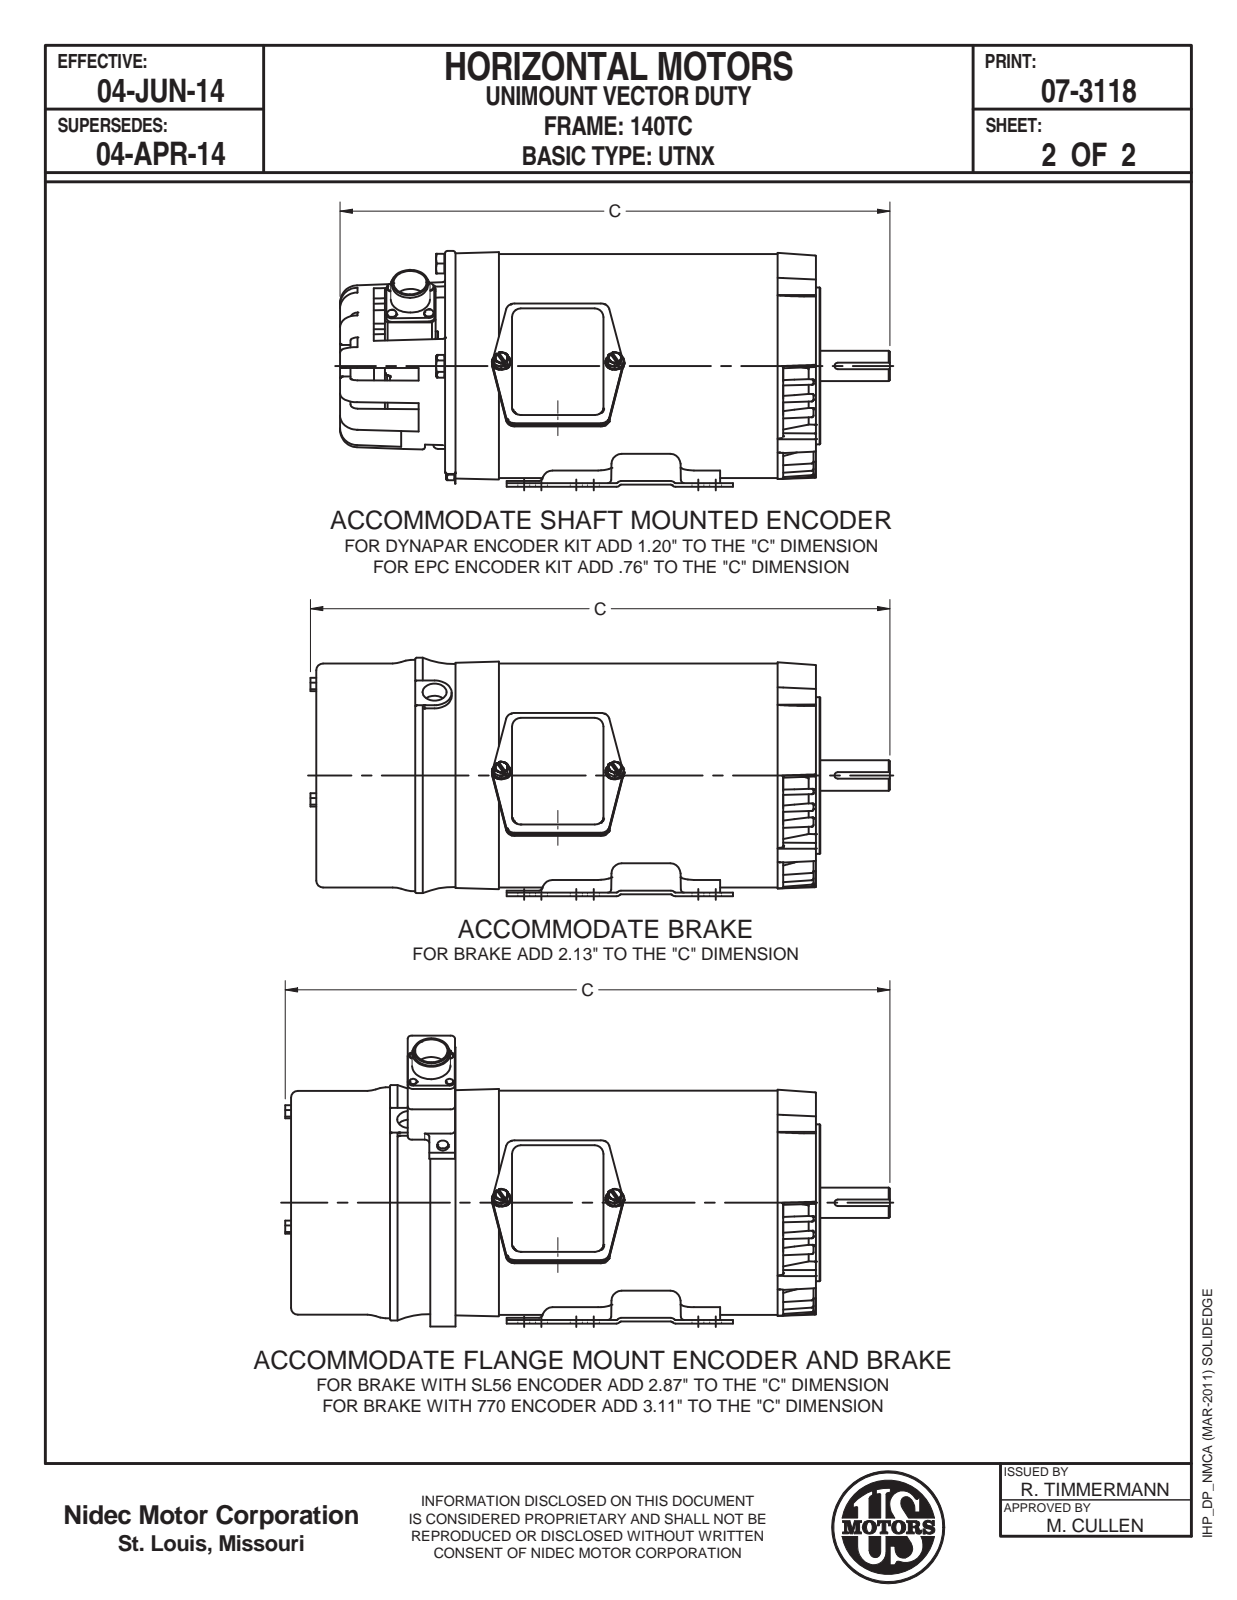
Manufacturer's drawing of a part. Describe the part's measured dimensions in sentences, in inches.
The part is named "UN1T3BC". Its 3-D file was written by "SolidWorks 2021 (AUTOMOTIVE_DESIGN)". It is 10 solids with 2525 faces: 486 planar, 538 cylindrical and 1501 other. Overall it measures 14.566 by 9.279 by 6.738 inches. Its volume is 56.92 cubic inches and its surface area 954 square inches. Round holes: 8 of diameter 0.25, 6 of diameter 0.344, 4 of diameter 0.302, 4 of diameter 0.406, 4 of diameter 0.421, 4 of diameter 0.55, 2 of diameter 0.098, 2 of diameter 0.173, 2 of diameter 0.229, 2 of diameter 0.281, 1 of diameter 0.725, 1 of diameter 0.875. Round bosses or shafts: 2 of diameter 0.325, 1 of diameter 6.5, 1 of diameter 6.44, 1 of diameter 6.315, 1 of diameter 4.5, 1 of diameter 1.191, 1 of diameter 1.177, 1 of diameter 1.16. Partial cylindrical surfaces (rounded edges, fillets, slot ends): 91 of radius 0.062, 71 of radius 0.031, 26 of radius 0.25, 18 of radius 0.202, 14 of radius 0.094, 12 of radius 0.048, 12 of radius 0.125, 12 of radius 0.172. The main face-to-face distances are 0.048, 0.104, 0.12, 0.53, 0.06, 10.141, 0.039, 10.344, 0.203, 10.18. The hole center spacings are 2.098, 2.246, 3.419, 4.349, 5.422, 1.187, 1.252, 1.75.
